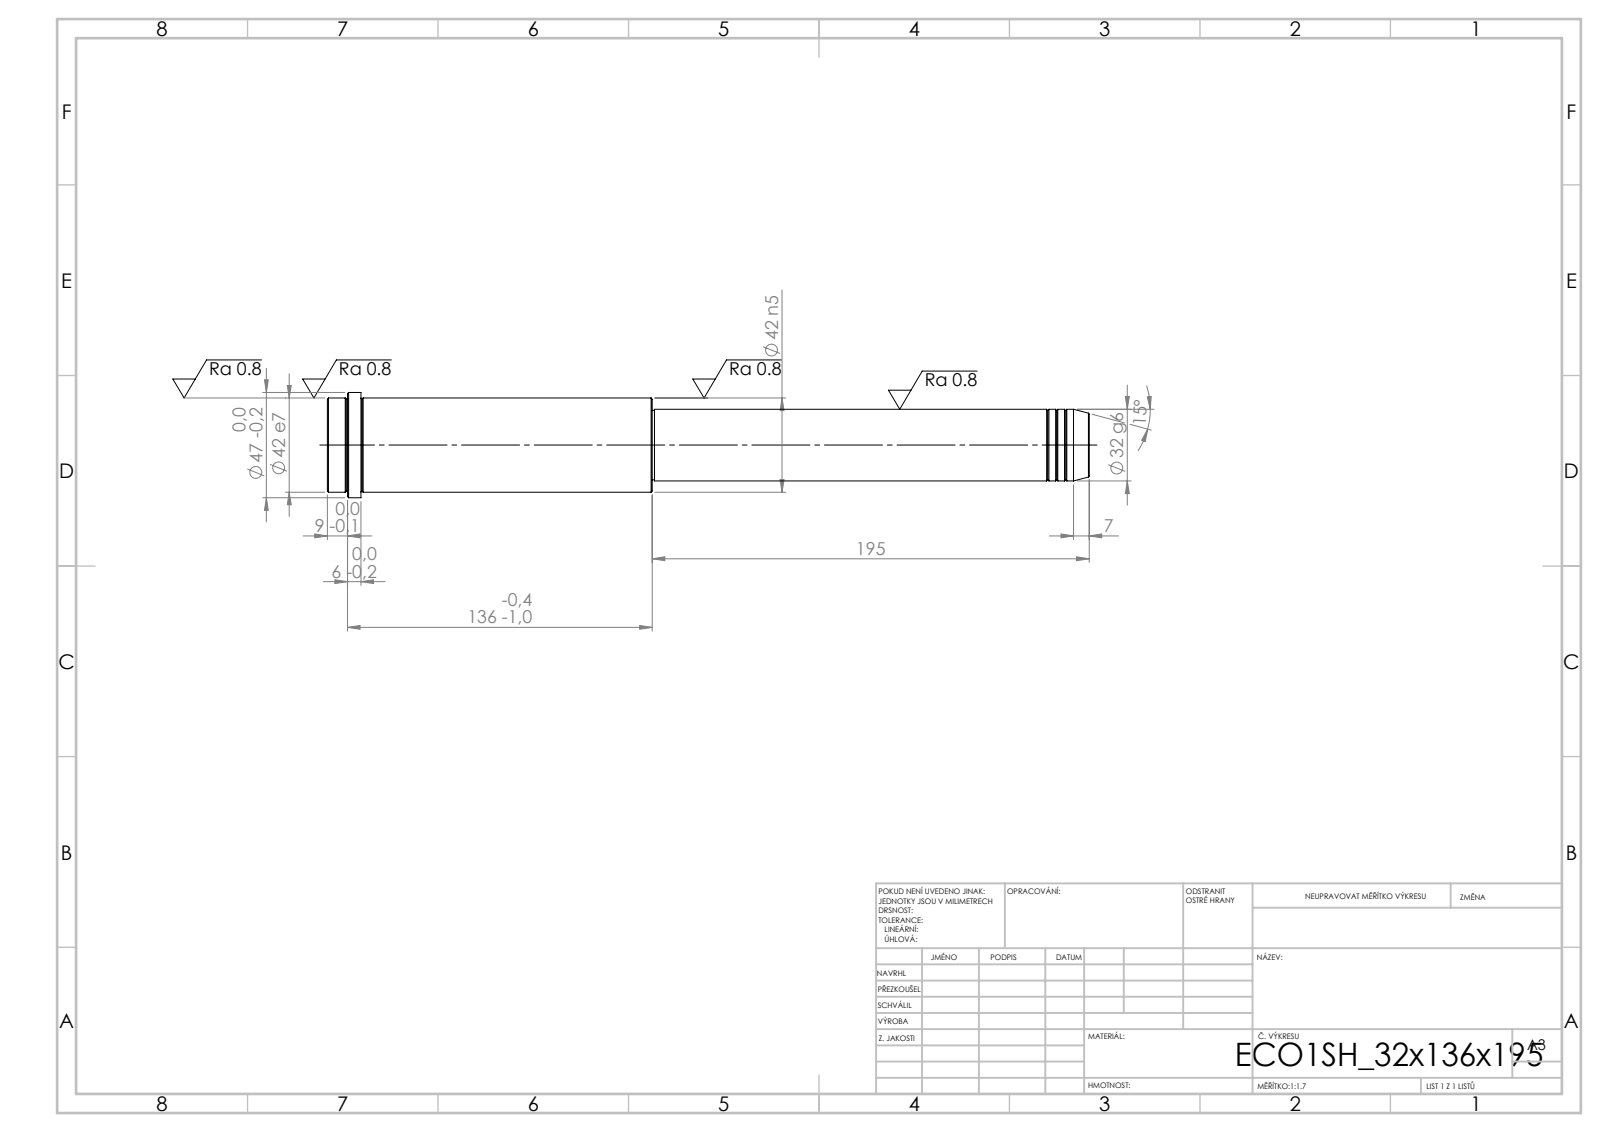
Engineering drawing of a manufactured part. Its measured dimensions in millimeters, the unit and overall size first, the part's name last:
Units: millimetres
Overall size (bounding box): 340 × 47 × 47
Round bosses / shafts (diameter × count): ⌀47 ×1, ⌀42 ×1, ⌀32 ×1, ⌀31 ×1
Main face-to-face distances: 340, 195, 145, 325, 130, 15, 331, 136, 6, 9
Volume: 358 858 mm³ · Surface area: 42 376 mm²
Bodies: 1 solid, 52 faces (6 planar, 16 cylindrical, 30 other)
STEP written by: SolidWorks 2019 (CONFIG_CONTROL_DESIGN)
